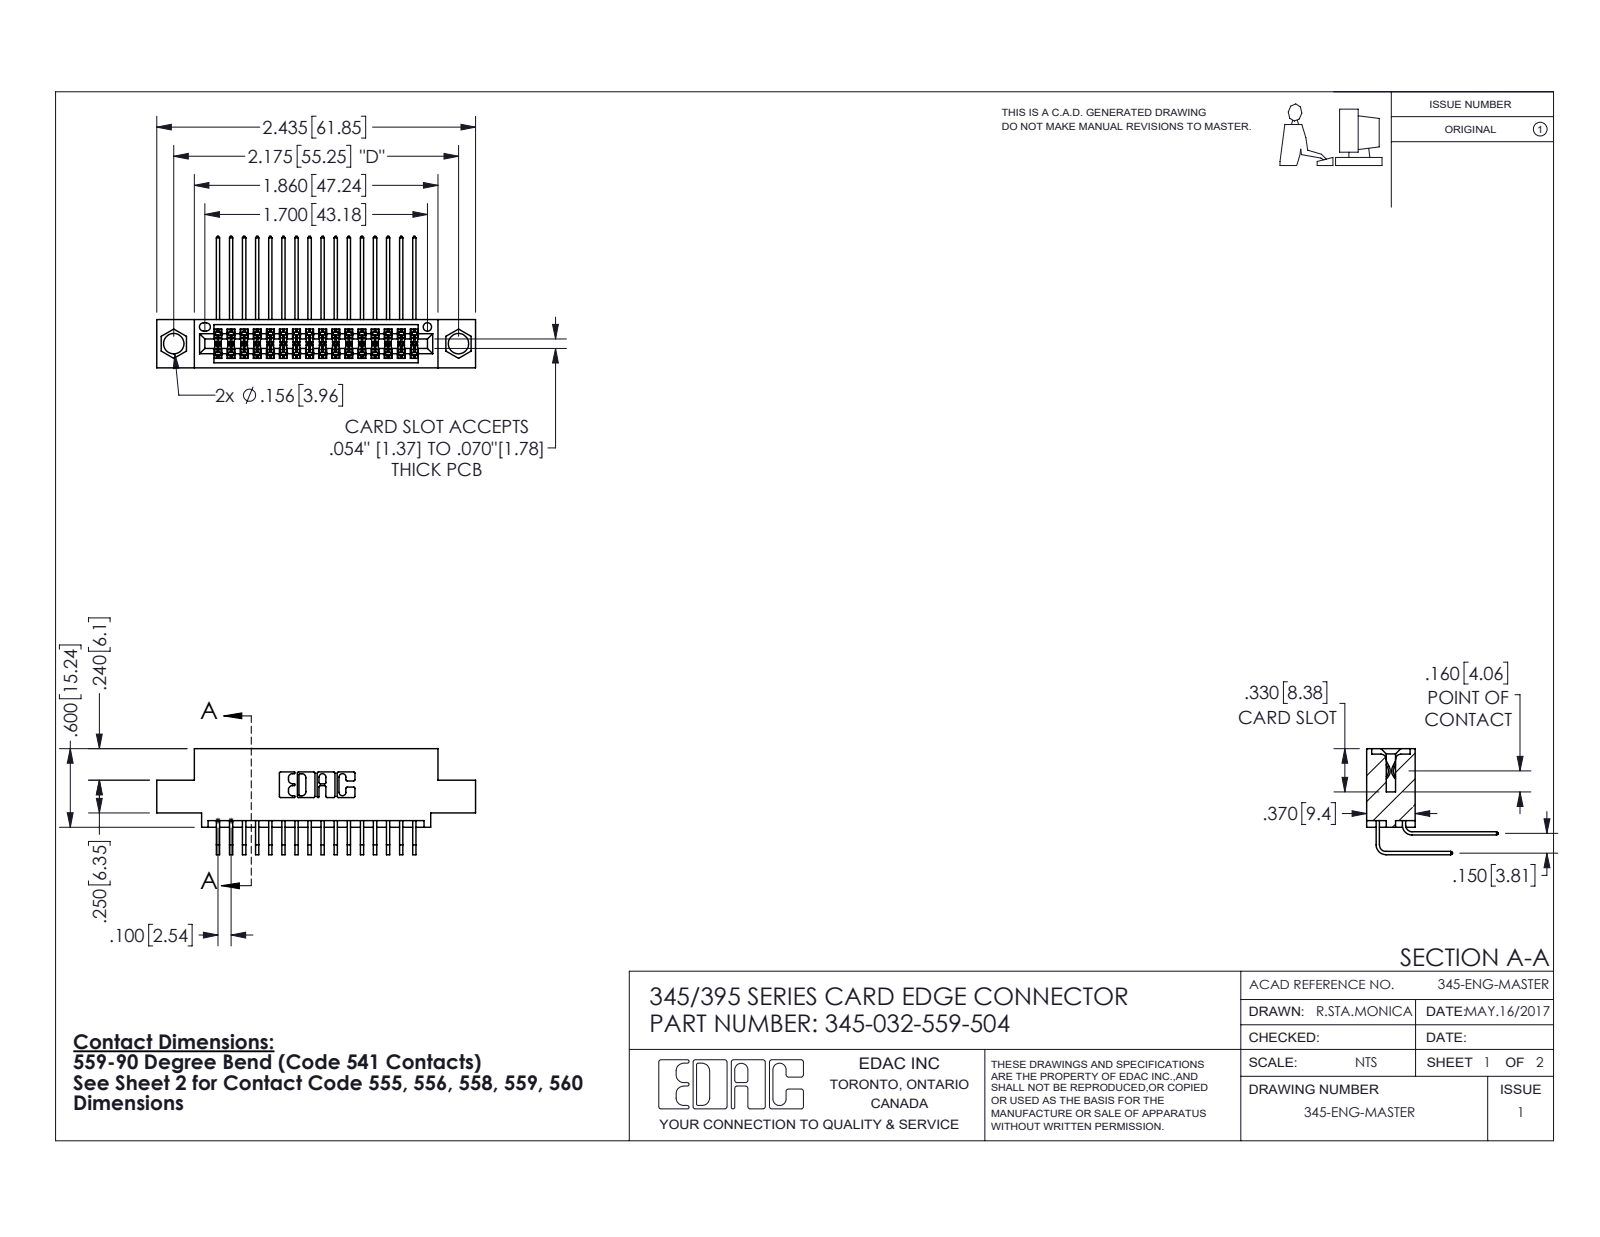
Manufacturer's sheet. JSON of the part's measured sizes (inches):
{"part_name": "345-292-001_559 Tail - 2; 345 Part_0.110 Offset - 0.156 Dia-TI; 345-032-559-504; 345-292-001_558 559 Tail - 1", "step_written_by": "SolidWorks 2020 (CONFIG_CONTROL_DESIGN)", "units": "inches", "bodies": {"solids": 33, "faces": 1808, "planar": 1218, "cylindrical": 590, "other": 0}, "overall_size": [2.435, 1.005, 0.809], "volume_in3": 0.352, "surface_area_in2": 13.7, "round_holes": [[0.156, 2], [0.064, 1]], "partial_cylinders_radius": [[0.006, 48], [0.01, 22], [0.007, 6], [0.031, 6], [0.026, 3], [0.014, 2], [0.019, 2], [0.022, 2]], "face_to_face_distances": [0.072, 0.298, 0.2, 0.37, 0.098, 0.272, 0.025, 0.225, 0.15, 0.175], "hole_center_spacings": [0.27, 1.942, 2.175]}
